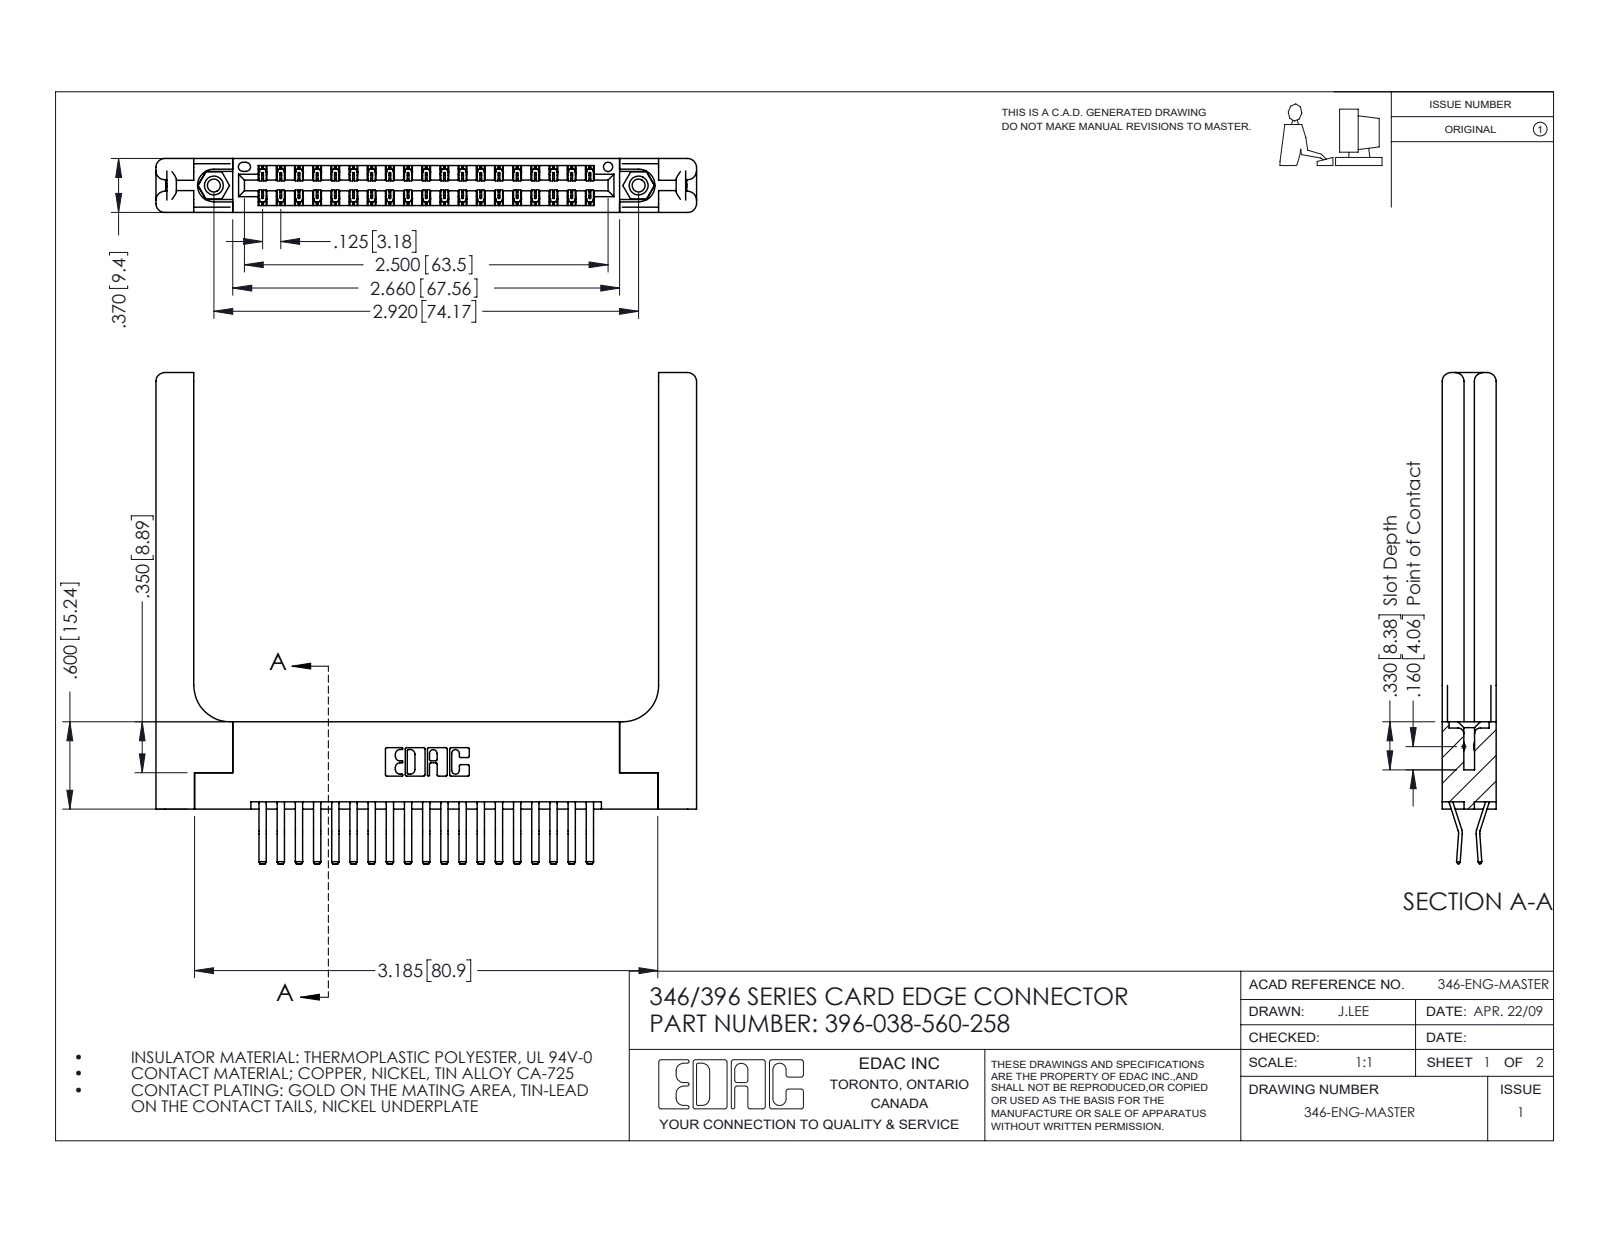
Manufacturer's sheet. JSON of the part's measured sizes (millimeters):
{"part_name": "396-038-560-258; 346-220-058_345-220-058; 346 Part_Flush Mounting Lugs - 0.156 Dia-TH; 345-292-001_560 Tail (+1 more)", "step_written_by": "SolidWorks 2016 (CONFIG_CONTROL_DESIGN)", "units": "millimeters", "bodies": {"solids": 43, "faces": 2430, "planar": 1554, "cylindrical": 816, "other": 60}, "overall_size": [94.4, 85.7, 9.4], "volume_mm3": 16760, "surface_area_mm2": 18030, "round_holes": [[2.3, 2], [3.2, 2], [4, 2], [1.6, 1]], "round_bosses_or_shafts": [[3.9, 2]], "partial_cylinders_radius": [[0.2, 57], [0.3, 22], [1.5, 16], [0.2, 6], [0.8, 6], [0.7, 3], [0.3, 2], [0.4, 2]], "face_to_face_distances": [9.4, 1.8, 3.8, 3.8, 1.2, 8.2, 0.6, 6.4, 2, 2.6], "hole_center_spacings": [6.2, 68.9, 74.2]}
